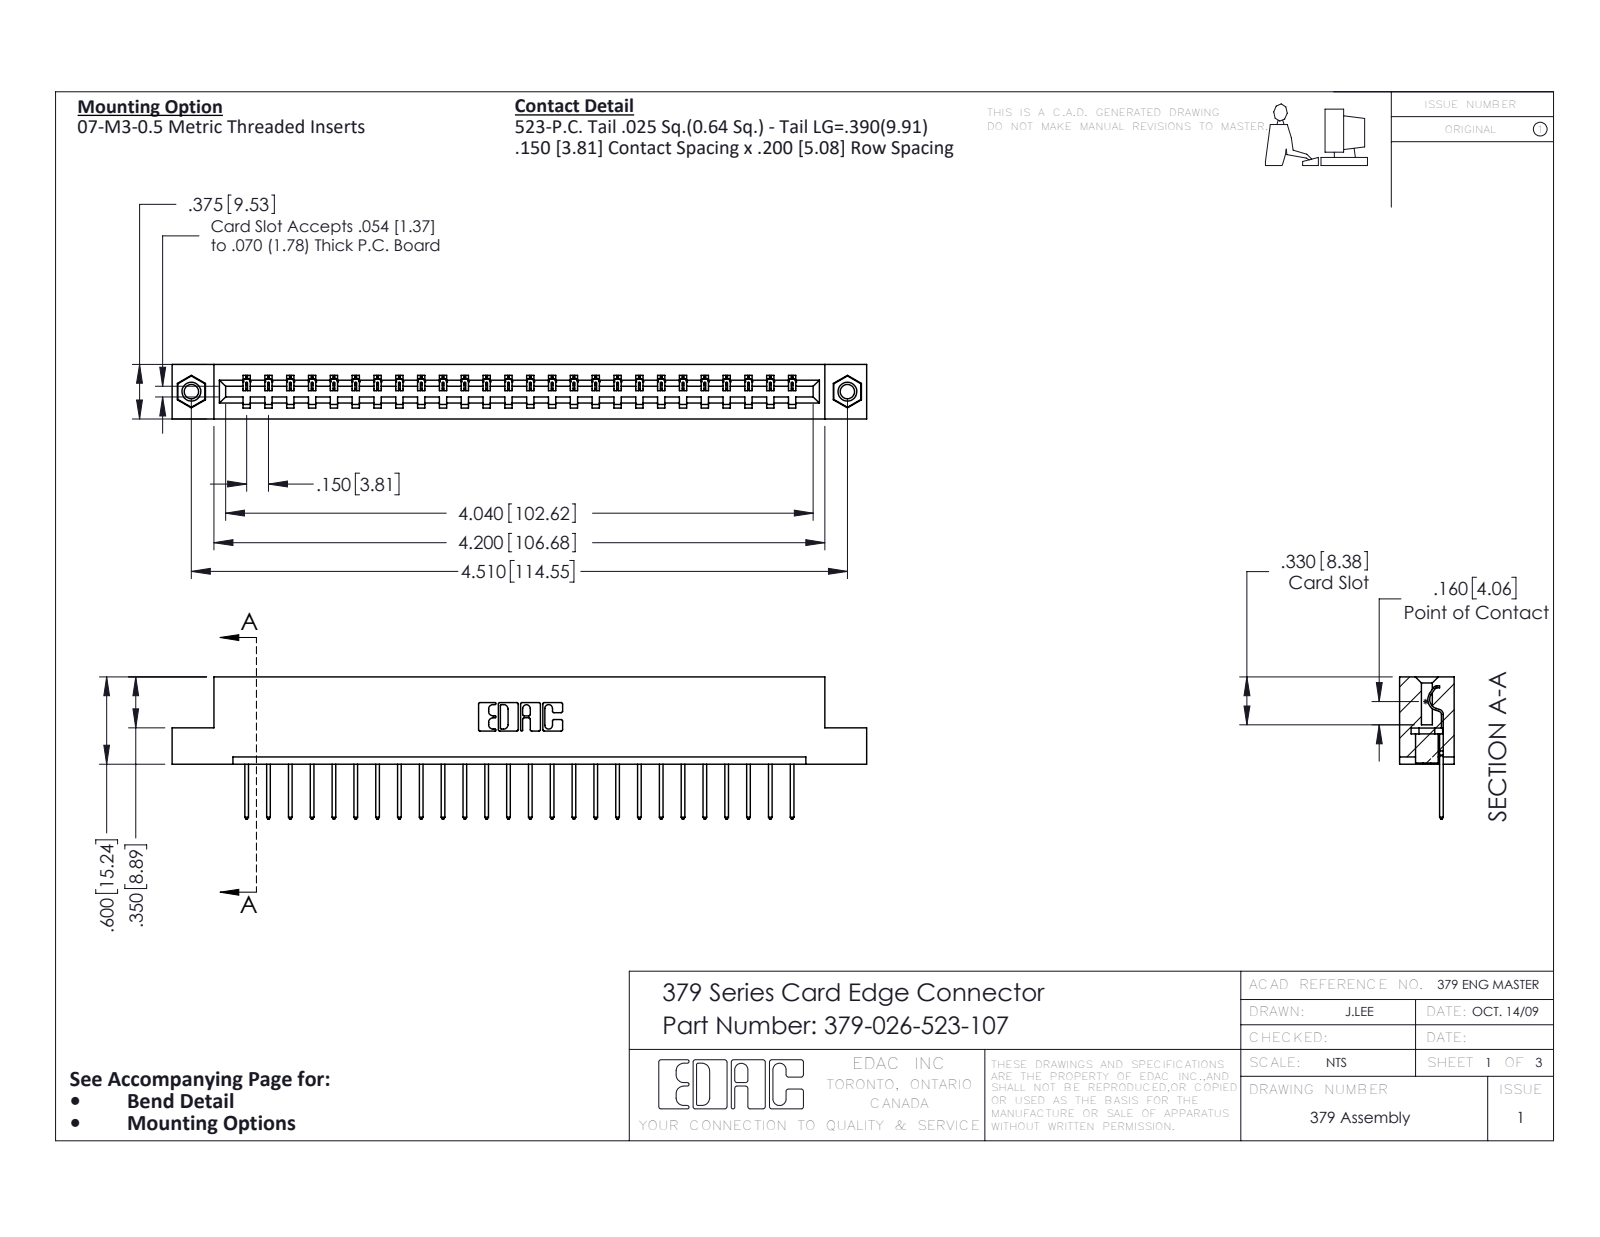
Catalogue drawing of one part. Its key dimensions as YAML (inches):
part_name: "345-250-001_345-250-005-103; 345-292-001_345-293-123; 379-026-523-107; 379 Part_Flush - .156 Dia - TI"
step_written_by: "SolidWorks 2016 (CONFIG_CONTROL_DESIGN)"
units: inches
bodies: {solids: 29, faces: 1682, planar: 1194, cylindrical: 472, other: 16}
overall_size: [4.775, 0.977, 0.375]
volume: 0.765
surface_area: 19.84
round_holes:
  - {diameter: 0.098, count: 2}
  - {diameter: 0.125, count: 2}
  - {diameter: 0.156, count: 2}
round_bosses_or_shafts:
  - {diameter: 0.155, count: 2}
partial_cylinders:
  - {radius: 0.006, count: 52}
  - {radius: 0.01, count: 52}
  - {radius: 0.01, count: 22}
  - {radius: 0.007, count: 6}
  - {radius: 0.031, count: 6}
  - {radius: 0.026, count: 3}
  - {radius: 0.014, count: 1}
  - {radius: 0.022, count: 1}
face_to_face_distances: [0.3, 0.075, 0.375, 0.225, 0.6, 0.2, 0.275, 0.1, 0.025, 0.15]
hole_center_spacings: [4.51]
